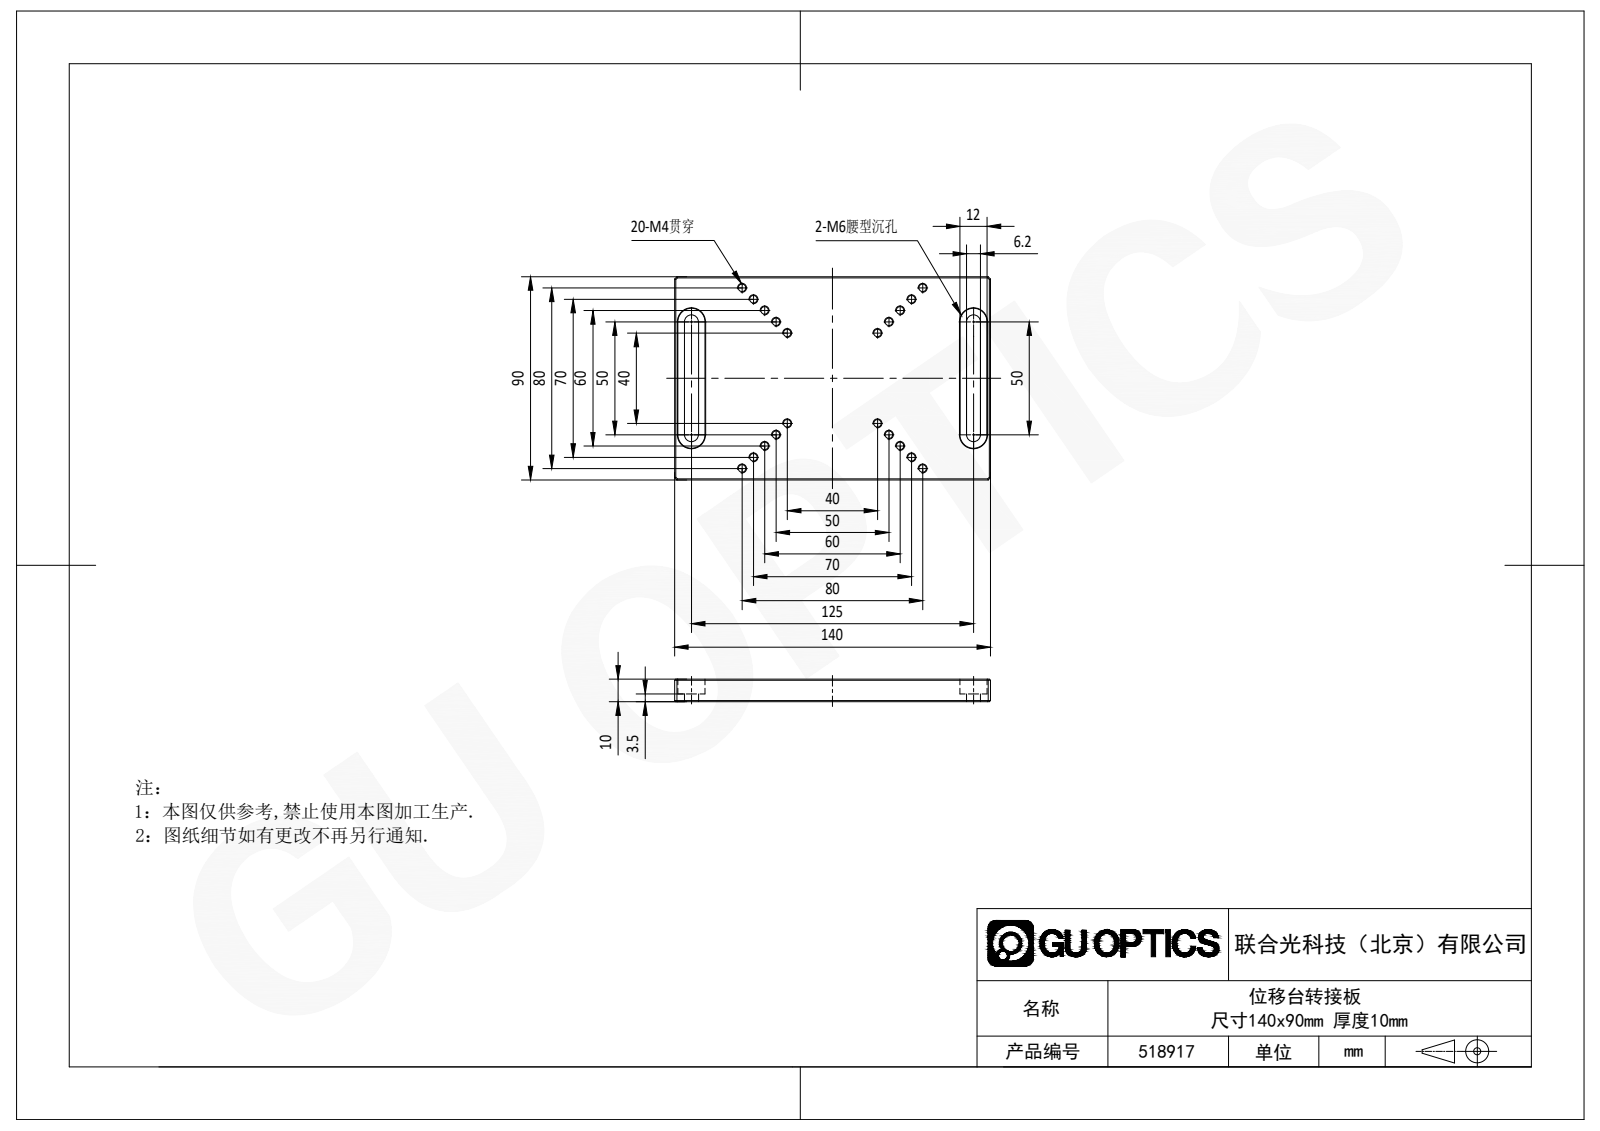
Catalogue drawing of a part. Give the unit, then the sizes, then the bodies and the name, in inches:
Units: inches
Overall size (bounding box): 5.512 × 3.543 × 0.394
Round holes (diameter × count): ⌀0.13 ×20
Partial cylindrical surfaces — rounded edges, fillets, slot ends (radius × count): R0.122 ×4, R0.236 ×4
Main face-to-face distances: 0.394, 3.543, 4.921, 5.512, 0.138, 0.256, 0.114, 0.358, 0.059, 0.531
Hole centre spacings: 0.278, 2.784, 0.557, 3.341, 0.835, 1.783, 2.007, 2.174
Volume: 6.864 in³ · Surface area: 50.25 in²
Bodies: 1 solid, 92 faces (40 planar, 28 cylindrical, 24 other)
STEP written by: SolidWorks 2020 (CONFIG_CONTROL_DESIGN)
